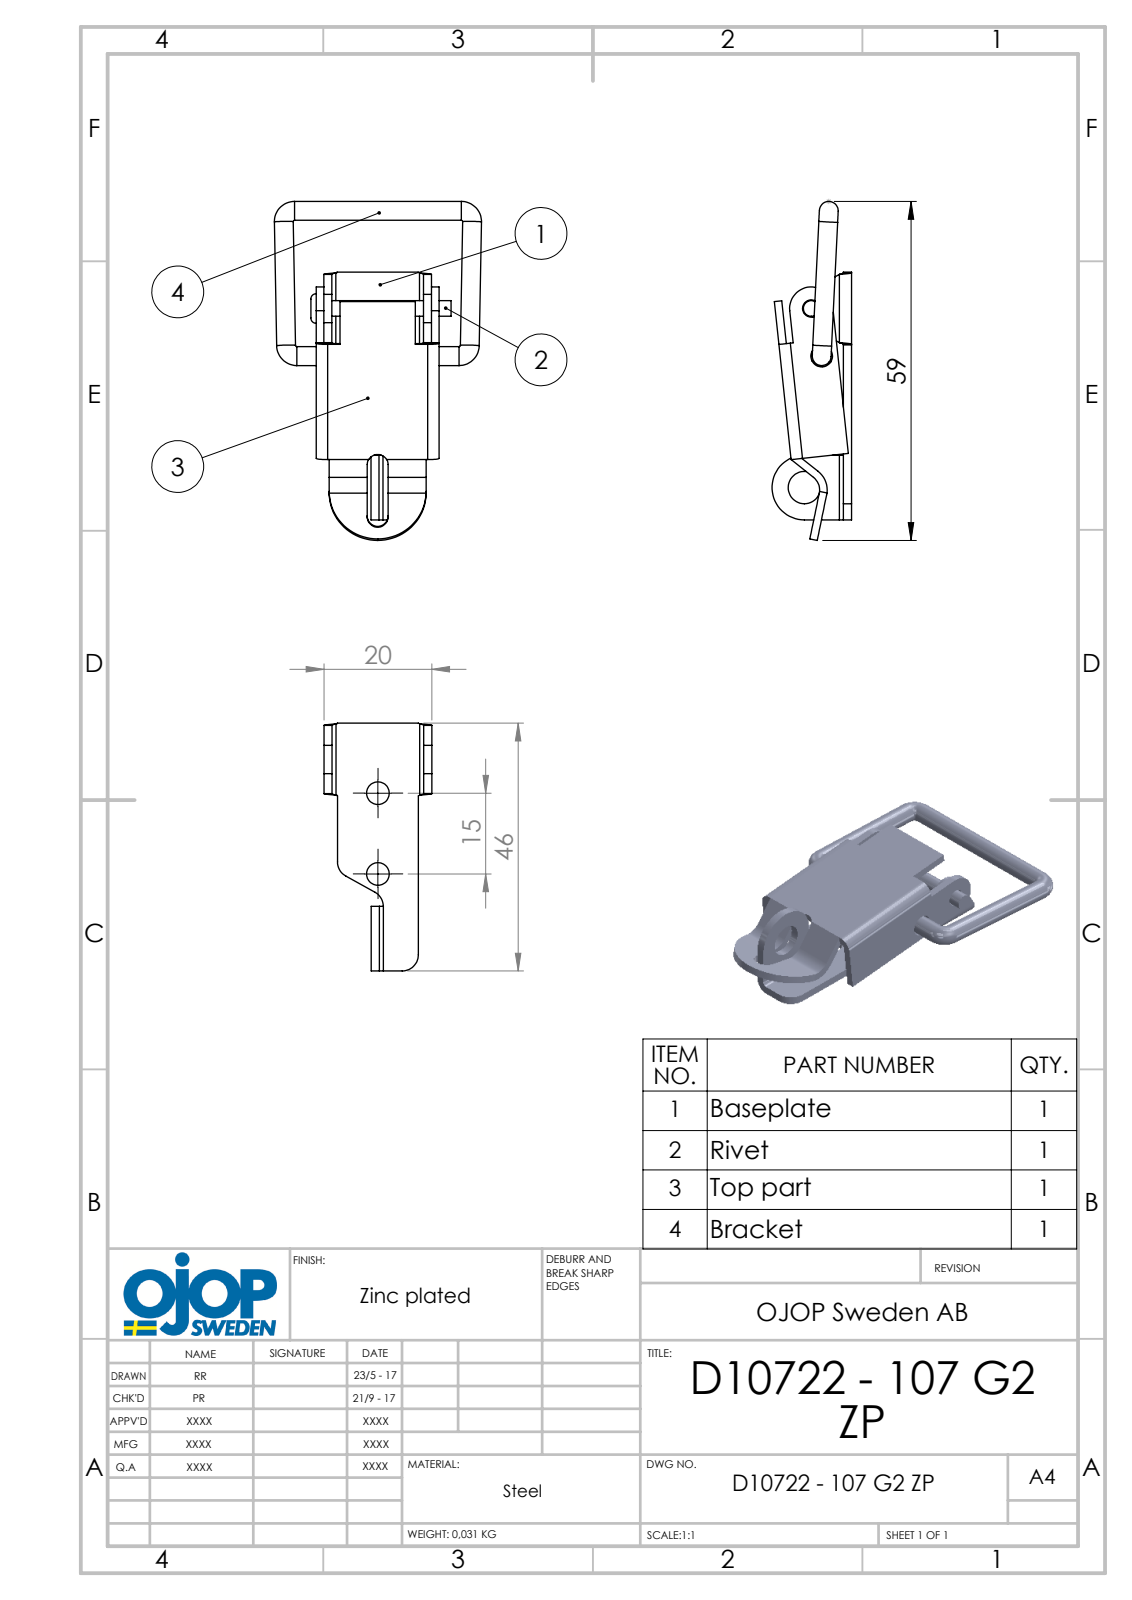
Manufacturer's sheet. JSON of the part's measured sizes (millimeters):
{"part_name": "D10722 - 107 G2 ZP; nit; Platta; bygel (+1 more)", "step_written_by": "SolidWorks 2015 (AUTOMOTIVE_DESIGN)", "units": "millimeters", "bodies": {"solids": 4, "faces": 152, "planar": 81, "cylindrical": 57, "other": 14}, "overall_size": [62.92, 38.42, 14.74], "volume_mm3": 4318, "surface_area_mm2": 6568, "round_holes": [[4.2, 2], [3.2, 1], [4, 1], [6, 1]], "round_bosses_or_shafts": [[3.5, 4], [2.9, 1]], "partial_cylinders_radius": [[0.74, 5], [3, 5], [2.24, 3], [1.95, 2], [2.14, 2], [4, 1], [4.4, 1], [6, 1]], "face_to_face_distances": [1.4, 1.5, 21.4, 20, 22.8, 9.74, 8.76, 19.9, 2.9, 18.5], "hole_center_spacings": [9.05, 15, 24.61, 33.26]}
